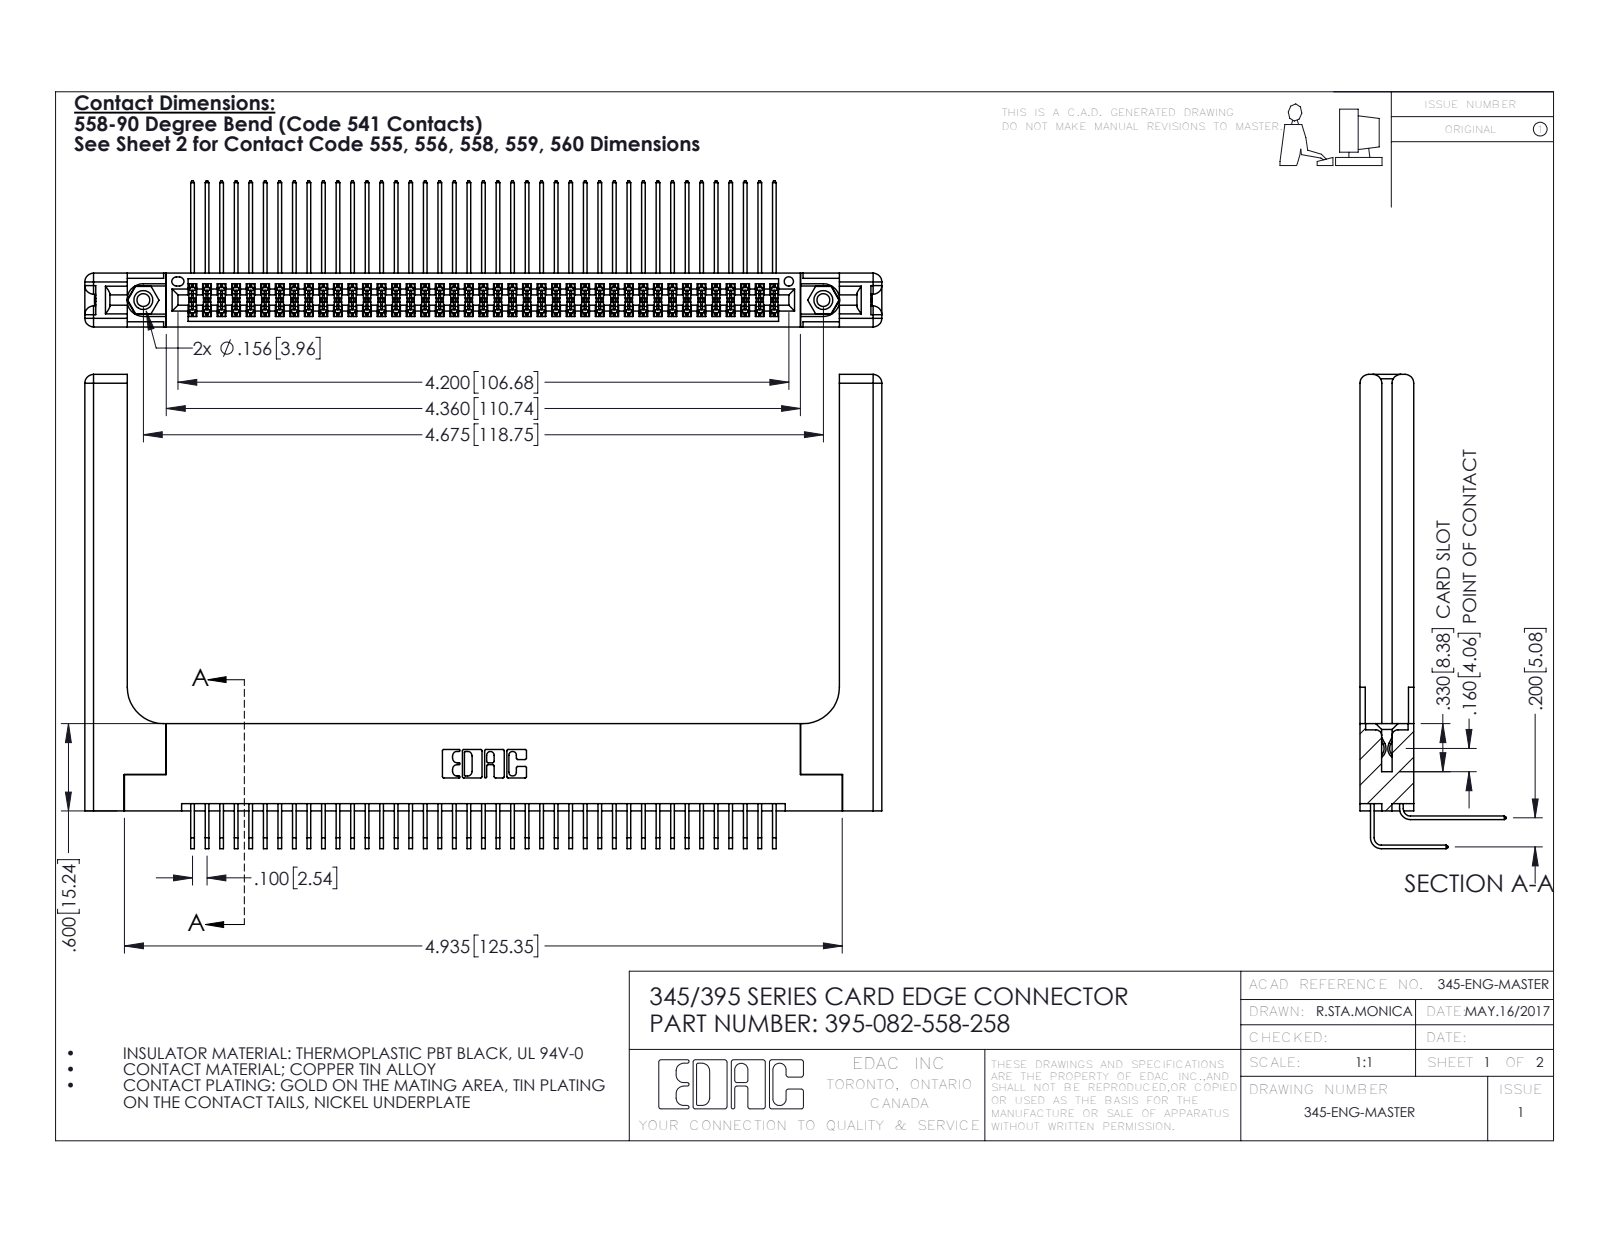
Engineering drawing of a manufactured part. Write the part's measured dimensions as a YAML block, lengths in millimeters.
part_name: "345-220-058_345-220-058; 395-082-558-258; 345 Part_Flush Mounting Lugs - 0.156 Dia-TH; 345-292-001_558 Tail - 2 (+2 more)"
step_written_by: "SolidWorks 2016 (CONFIG_CONTROL_DESIGN)"
units: millimeters
bodies: {solids: 87, faces: 4646, planar: 3098, cylindrical: 1488, other: 60}
overall_size: [139.2, 82.8, 25.5]
volume: 22450
surface_area: 27940
round_holes:
  - {diameter: 2.3, count: 2}
  - {diameter: 3.2, count: 2}
  - {diameter: 4, count: 2}
  - {diameter: 1.6, count: 1}
round_bosses_or_shafts:
  - {diameter: 3.9, count: 2}
partial_cylinders:
  - {radius: 0.2, count: 124}
  - {radius: 0.3, count: 22}
  - {radius: 1.5, count: 16}
  - {radius: 0.2, count: 6}
  - {radius: 0.8, count: 6}
  - {radius: 0.7, count: 3}
  - {radius: 0.4, count: 2}
  - {radius: 0.5, count: 2}
face_to_face_distances: [1.8, 9.4, 7.6, 5.1, 2.5, 6.9, 0.6, 5.7, 3.8, 3.8]
hole_center_spacings: [6.9, 112.8, 118.7]
